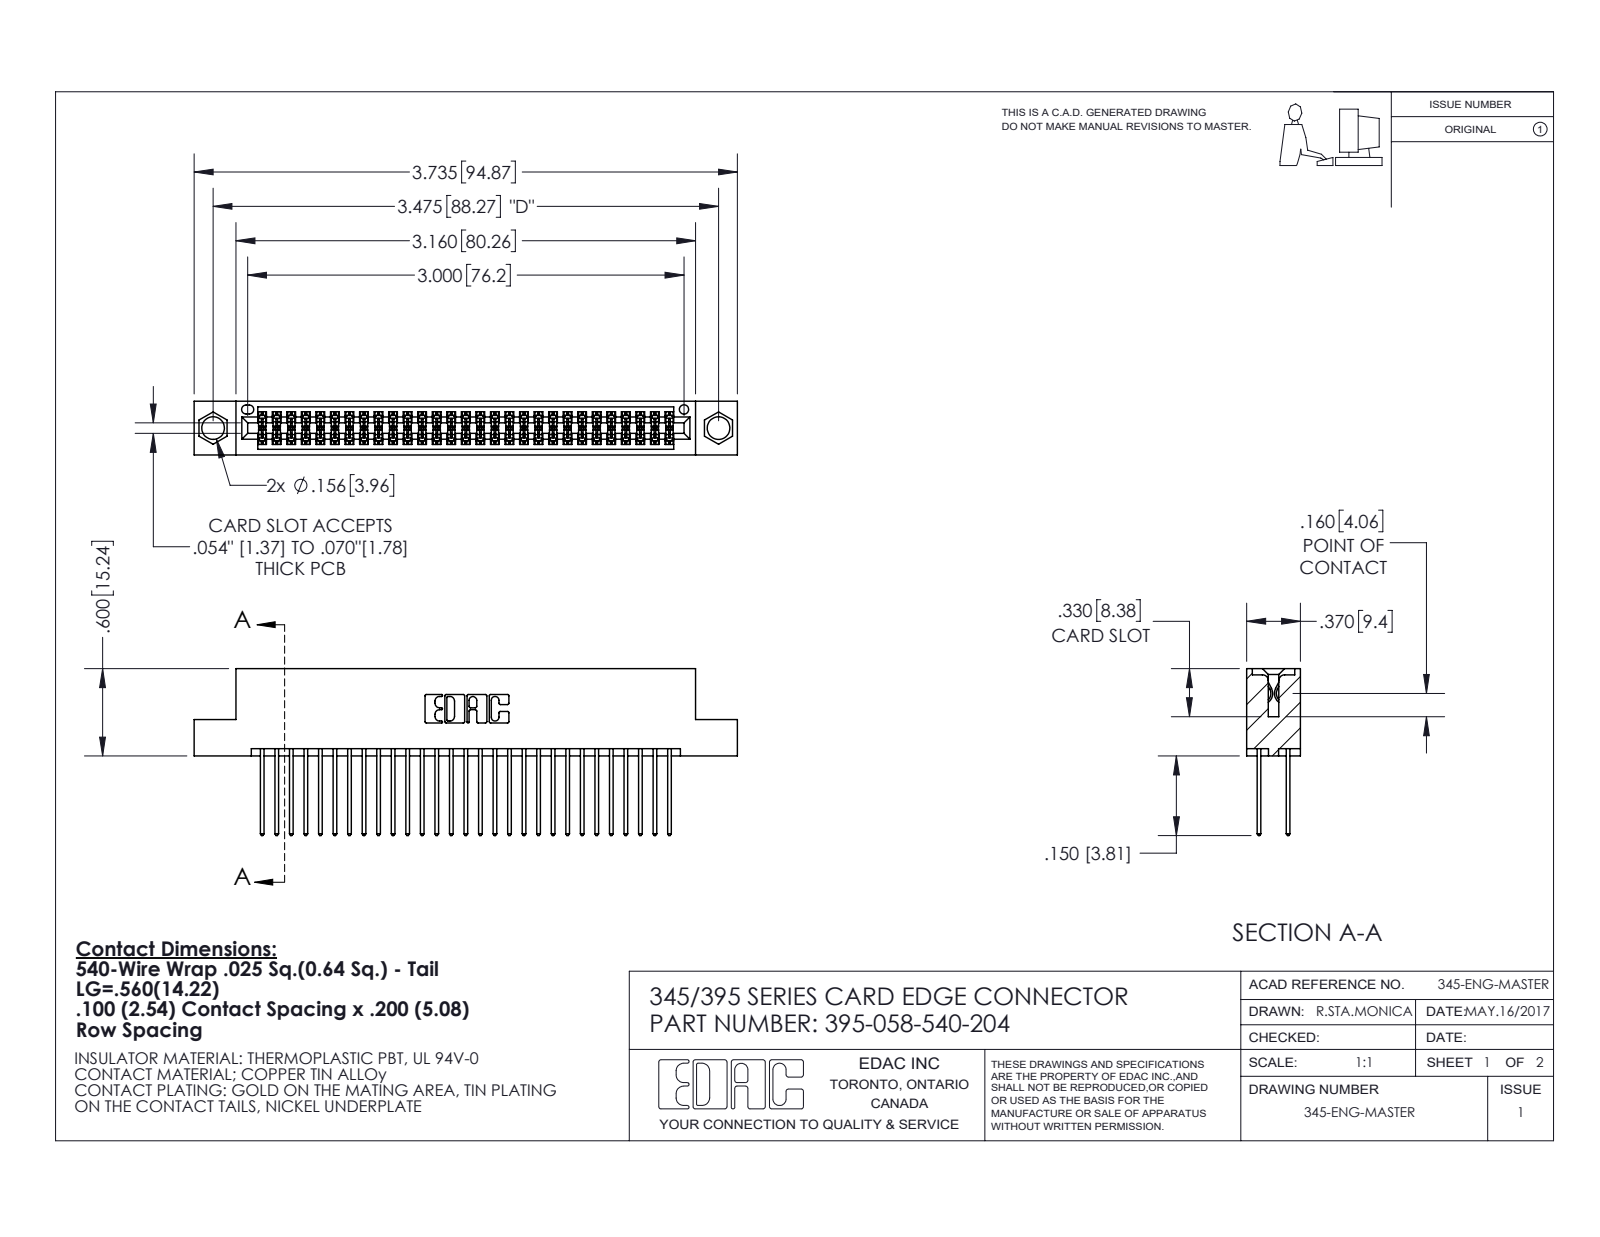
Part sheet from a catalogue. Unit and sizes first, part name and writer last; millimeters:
Units: millimetres
Overall size (bounding box): 94.9 × 29.1 × 9.4
Round holes (diameter × count): ⌀4 ×2, ⌀1.6 ×1
Partial cylindrical surfaces — rounded edges, fillets, slot ends (radius × count): R0.2 ×116, R0.3 ×58, R0.3 ×22, R0.2 ×6, R0.8 ×6, R0.7 ×3, R0.4 ×2, R0.5 ×2
Main face-to-face distances: 1.8, 7.6, 5.1, 2.5, 6.9, 0.6, 9.4, 5.7, 4.4, 3.8
Hole centre spacings: 6.9, 82.3, 88.3
Volume: 9 210 mm³ · Surface area: 14 230 mm²
Bodies: 59 solids, 3040 faces (2008 planar, 1032 cylindrical, 0 other)
Part name (STEP PRODUCT): 345-292-001_345-293-140; 395-058-540-204; 345 Part_Flush Mounting Lugs - 0.156 Dia-TI
STEP written by: SolidWorks 2020 (CONFIG_CONTROL_DESIGN)
